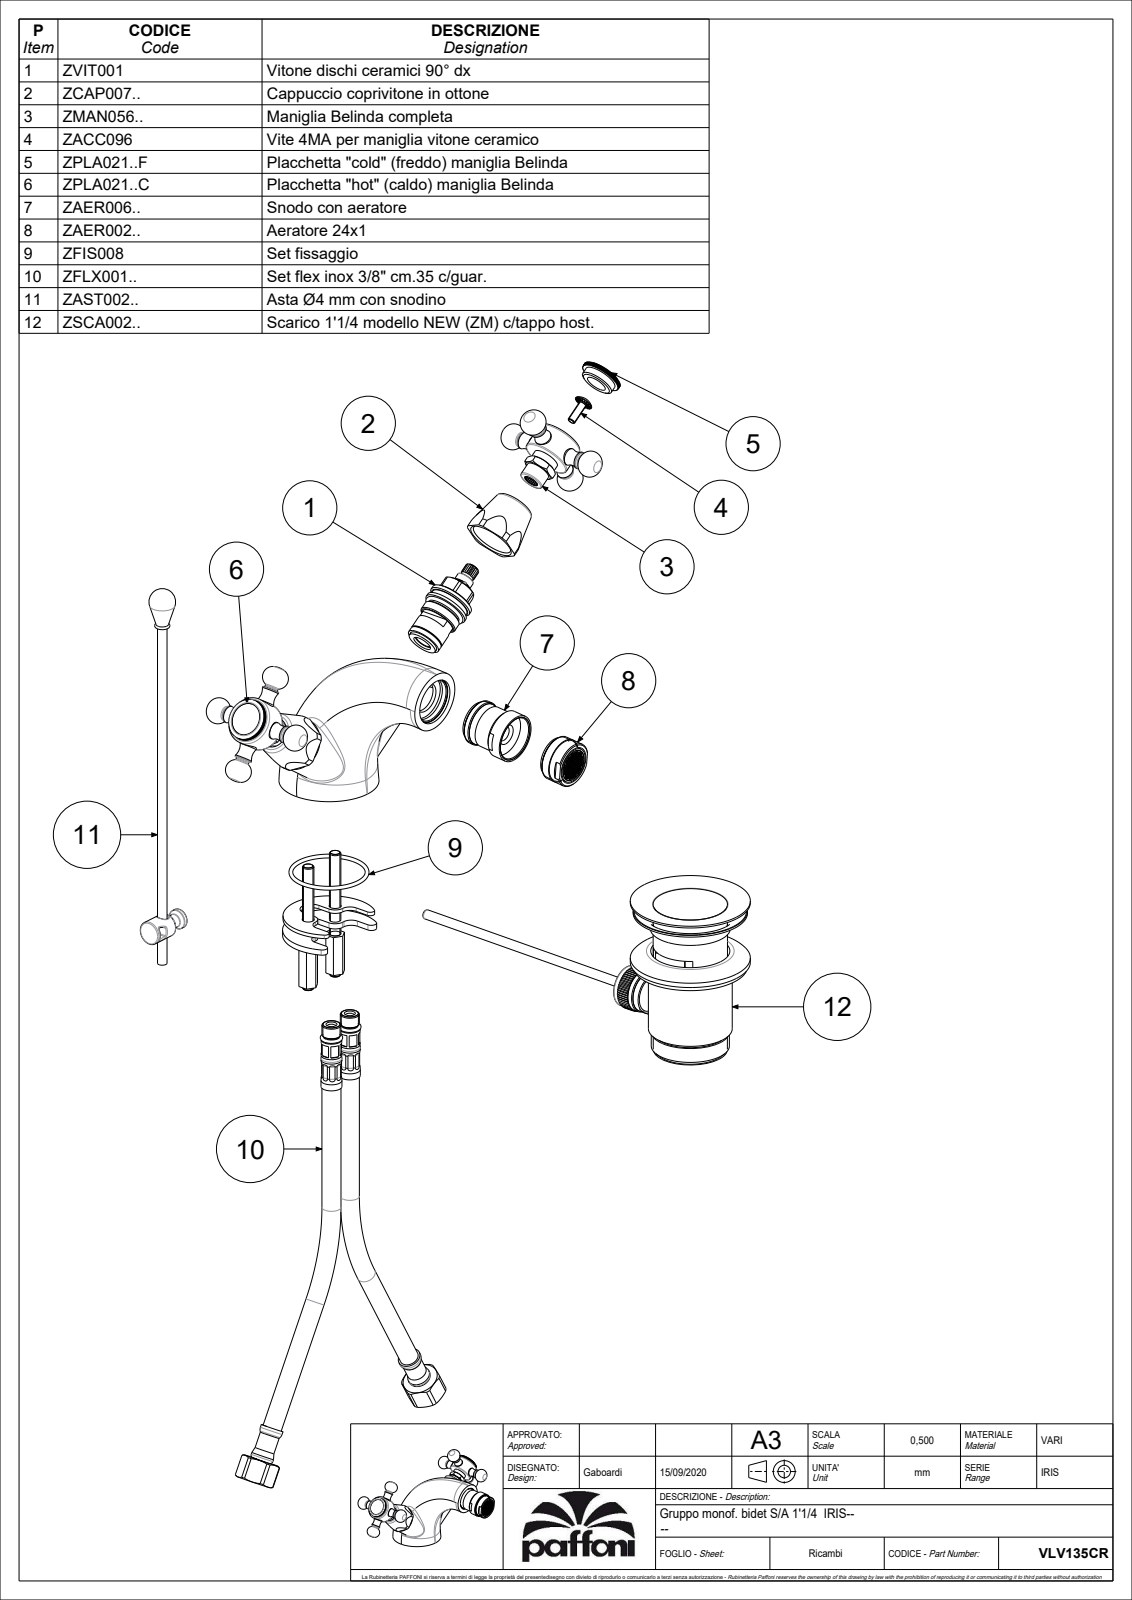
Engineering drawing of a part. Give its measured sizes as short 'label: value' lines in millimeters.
name: VLV135CR
written by: CREO PARAMETRIC BY PTC INC, 2020044 (CONFIG_CONTROL_DESIGN)
unit: mm
bodies: 3 solids, 1031 faces (495 planar, 322 cylindrical, 214 other)
size: 180.18 × 128.34 × 87.21
volume: 224 994 mm³; area: 45 399 mm²
holes: 3× ⌀5.5, 2× ⌀7, 2× ⌀9, 2× ⌀11, 2× ⌀18.6, 2× ⌀21.5, 1× ⌀42.5
bosses: 6× ⌀9, 6× ⌀7, 2× ⌀27.5, 2× ⌀25, 2× ⌀14, 2× ⌀13, 1× ⌀37.5, 1× ⌀25.8
rounds: 2× R11, 2× R14.5
face distances: 35.32, 26.5, 57.2, 21.88, 28.7, 3, 25.7, 11.2, 24.12, 46
hole spacings: 10.97, 12.08, 13.46, 13.6, 22.3, 22.61, 13, 15
